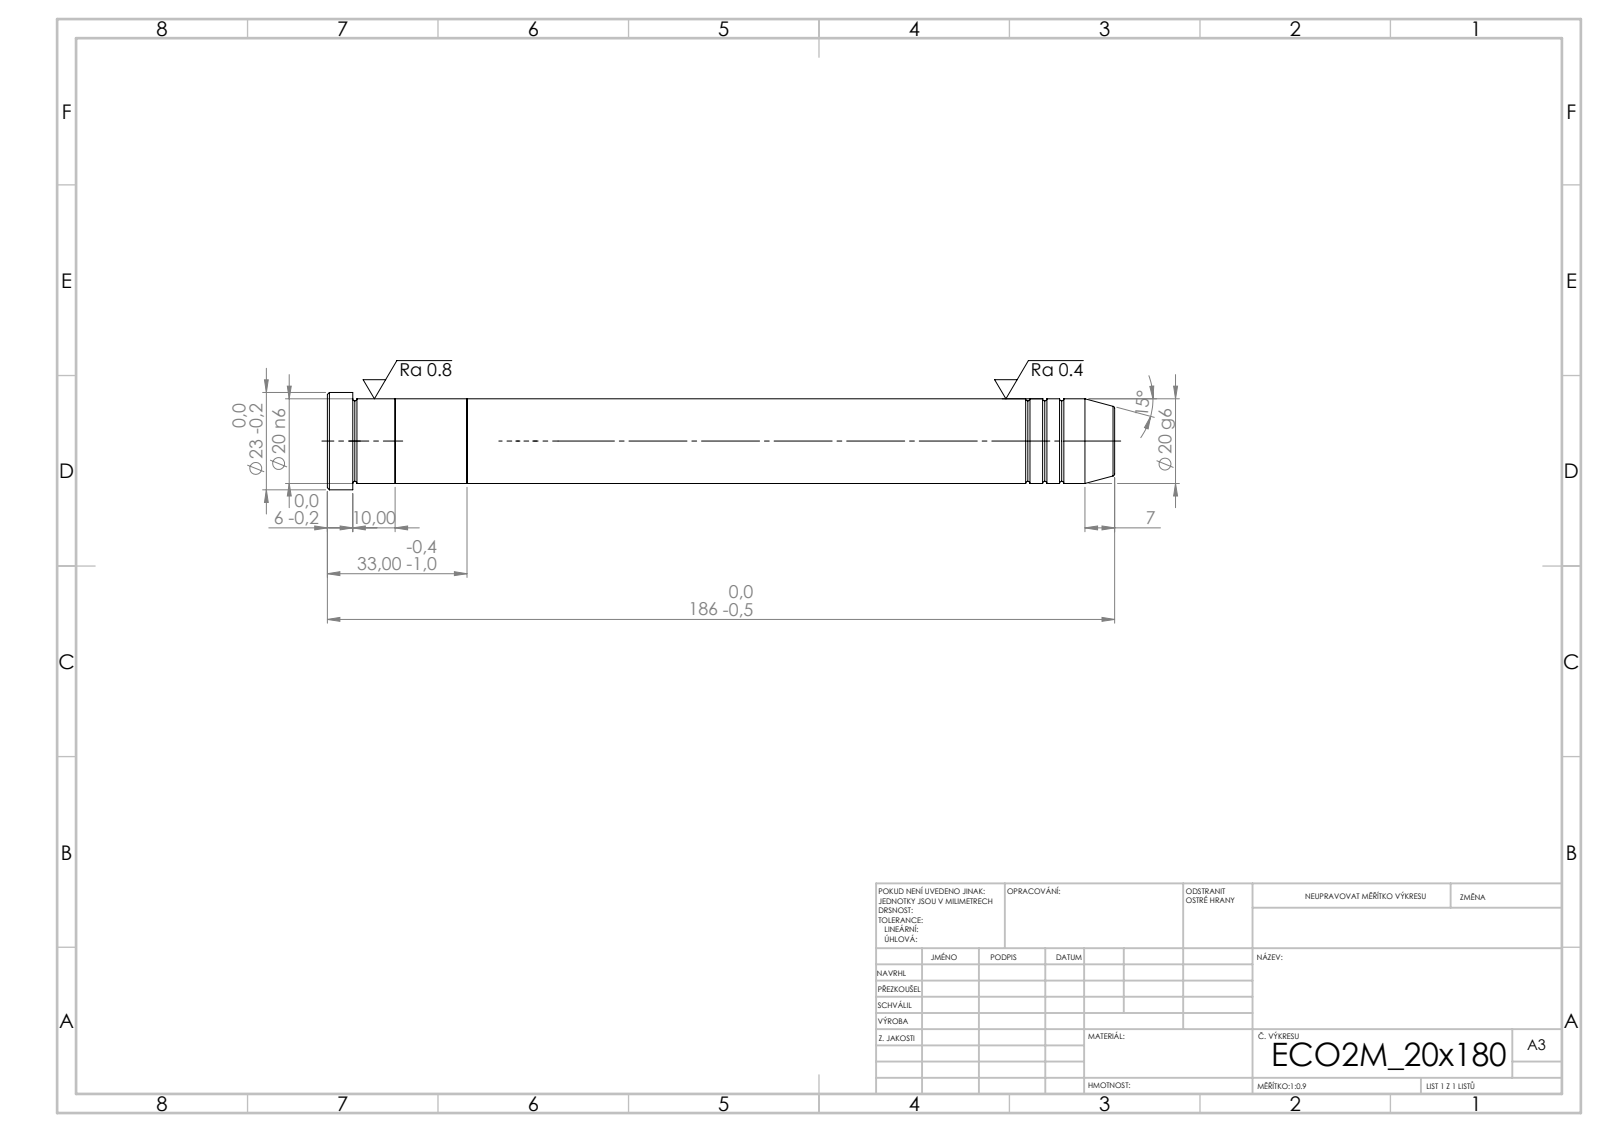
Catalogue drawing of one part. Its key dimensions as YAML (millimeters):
step_written_by: "SolidWorks 2019 (CONFIG_CONTROL_DESIGN)"
units: millimeters
bodies: {solids: 3, faces: 43, planar: 7, cylindrical: 14, other: 22}
overall_size: [186, 23, 23]
volume: 58548
surface_area: 13800
round_bosses_or_shafts:
  - {diameter: 23, count: 1}
  - {diameter: 20, count: 1}
face_to_face_distances: [17, 33, 16, 153, 170, 186, 180, 27, 10, 6]
